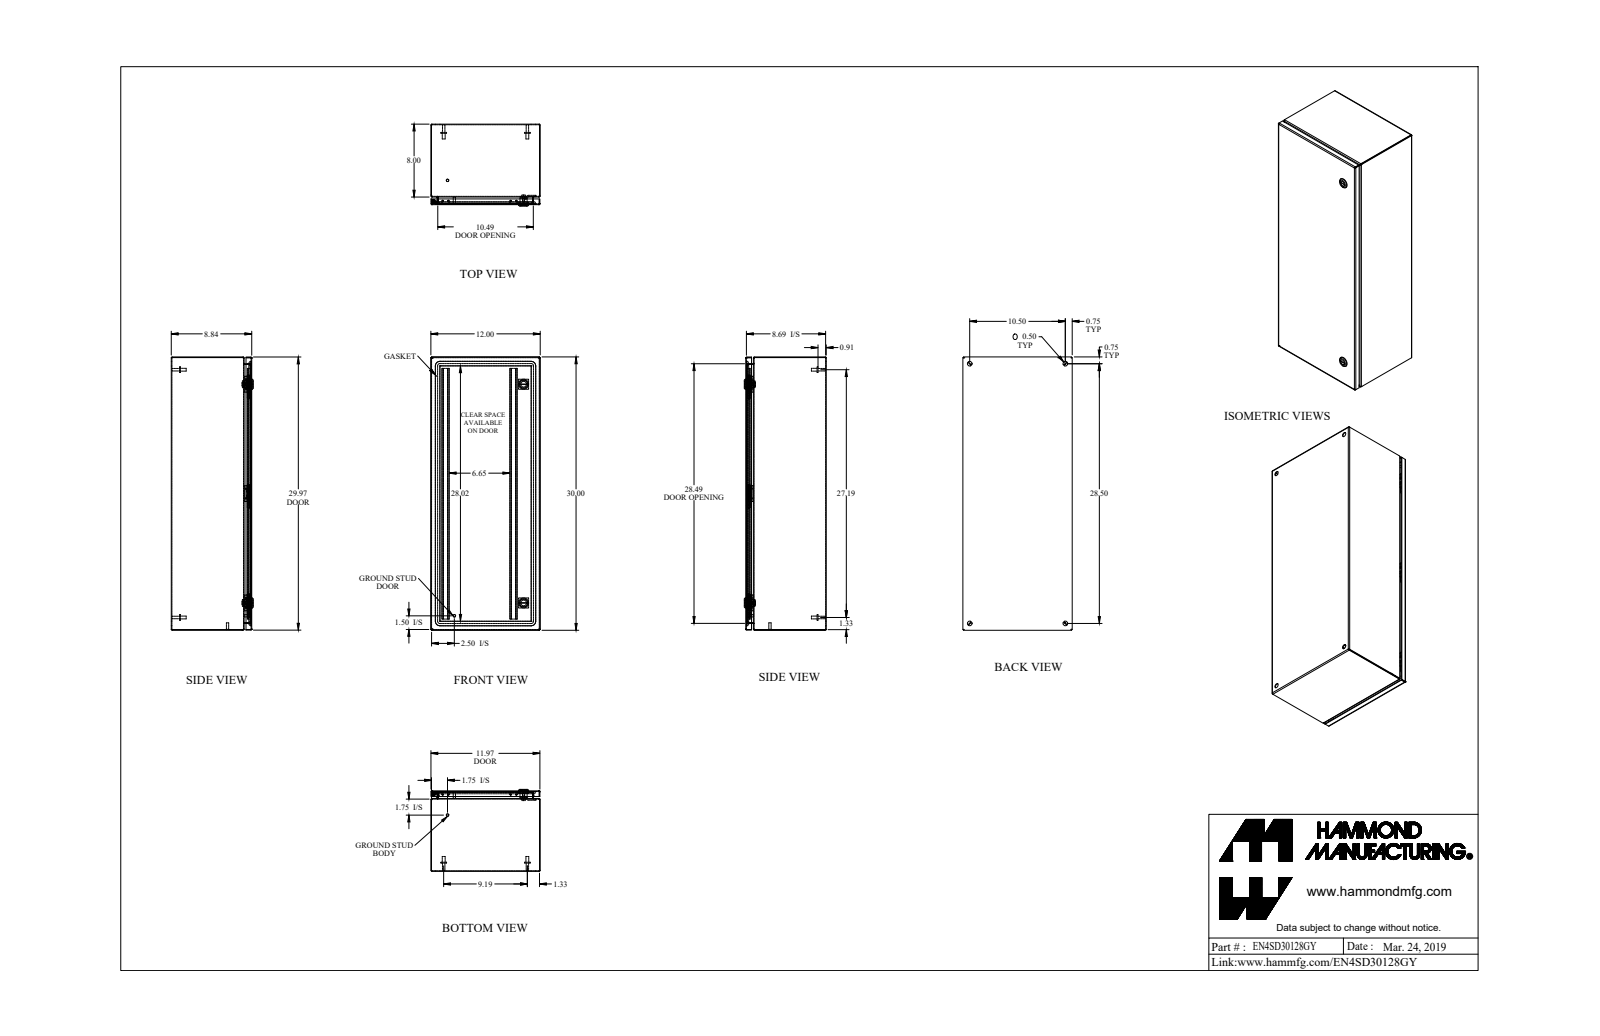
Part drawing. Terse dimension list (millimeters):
name: EN4SD30128GY_Default
written by: SolidWorks 2019 (CONFIG_CONTROL_DESIGN)
unit: mm
bodies: 31 solids, 885 faces (422 planar, 295 cylindrical, 168 other)
size: 762 × 304.8 × 228.5
volume: 2 039 000 mm³; area: 2 269 000 mm²
holes: 4× ⌀12.7, 2× ⌀5.9, 2× ⌀6.1, 2× ⌀15.9, 2× ⌀19.9, 1× ⌀4.4, 1× ⌀6.1
bosses: 4× ⌀15.9, 4× ⌀8, 4× ⌀6.9, 2× ⌀27.9, 2× ⌀13.3, 2× ⌀9, 2× ⌀7.1, 2× ⌀6.4
rounds: 20× R0.9, 20× R2.7, 12× R1.1, 12× R2.1, 12× R9.7, 8× R482.7, 6× R0.2, 6× R1.6
face distances: 1.8, 222.6, 303, 220.8, 224.5, 301.1, 304.8, 760.2, 21.3, 201.4
hole spacings: 246.2, 266.7, 723.9, 771.5, 63.3, 63.3, 609.6, 667.3
